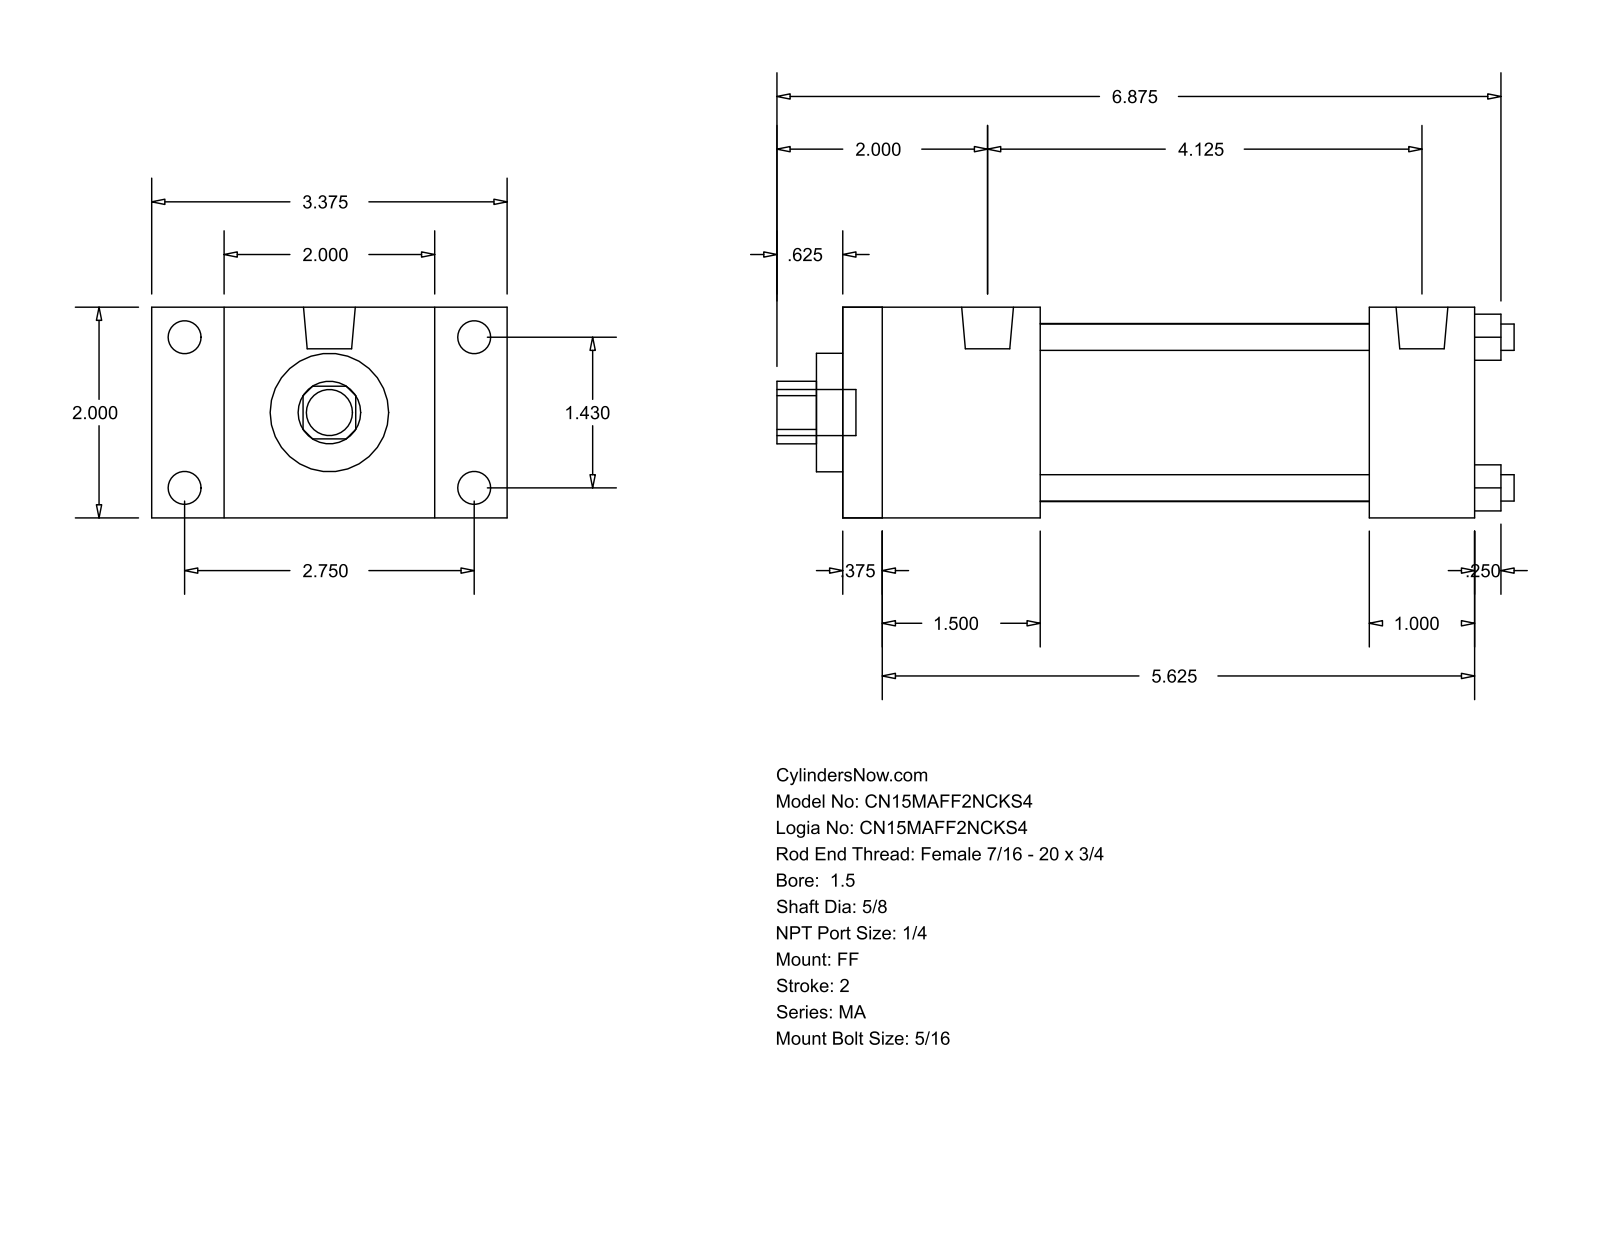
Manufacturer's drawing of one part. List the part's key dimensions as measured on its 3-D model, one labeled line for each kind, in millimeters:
Part name (STEP PRODUCT): MA_FF__0150_0.625
STEP written by: GSSL Pune (CONFIG_CONTROL_DESIGN)
Units: millimetres
Bodies: 0 solids, 92 faces (64 planar, 28 cylindrical, 0 other)
Overall size (bounding box): 177.8 × 85.72 × 50.8
Round holes (diameter × count): ⌀6.35 ×4, ⌀15.88 ×1, ⌀28.57 ×1, ⌀42.93 ×1
Round bosses / shafts (diameter × count): ⌀7.94 ×8, ⌀12.49 ×2, ⌀11.11 ×1
Partial cylindrical surfaces — rounded edges, fillets, slot ends (radius × count): R7.54 ×1
Main face-to-face distances: 50.8, 152.4, 9.52, 142.88, 25.4, 47.62, 127, 38.1, 117.48, 79.38
Hole centre spacings: 25.68, 36.32, 51.36
